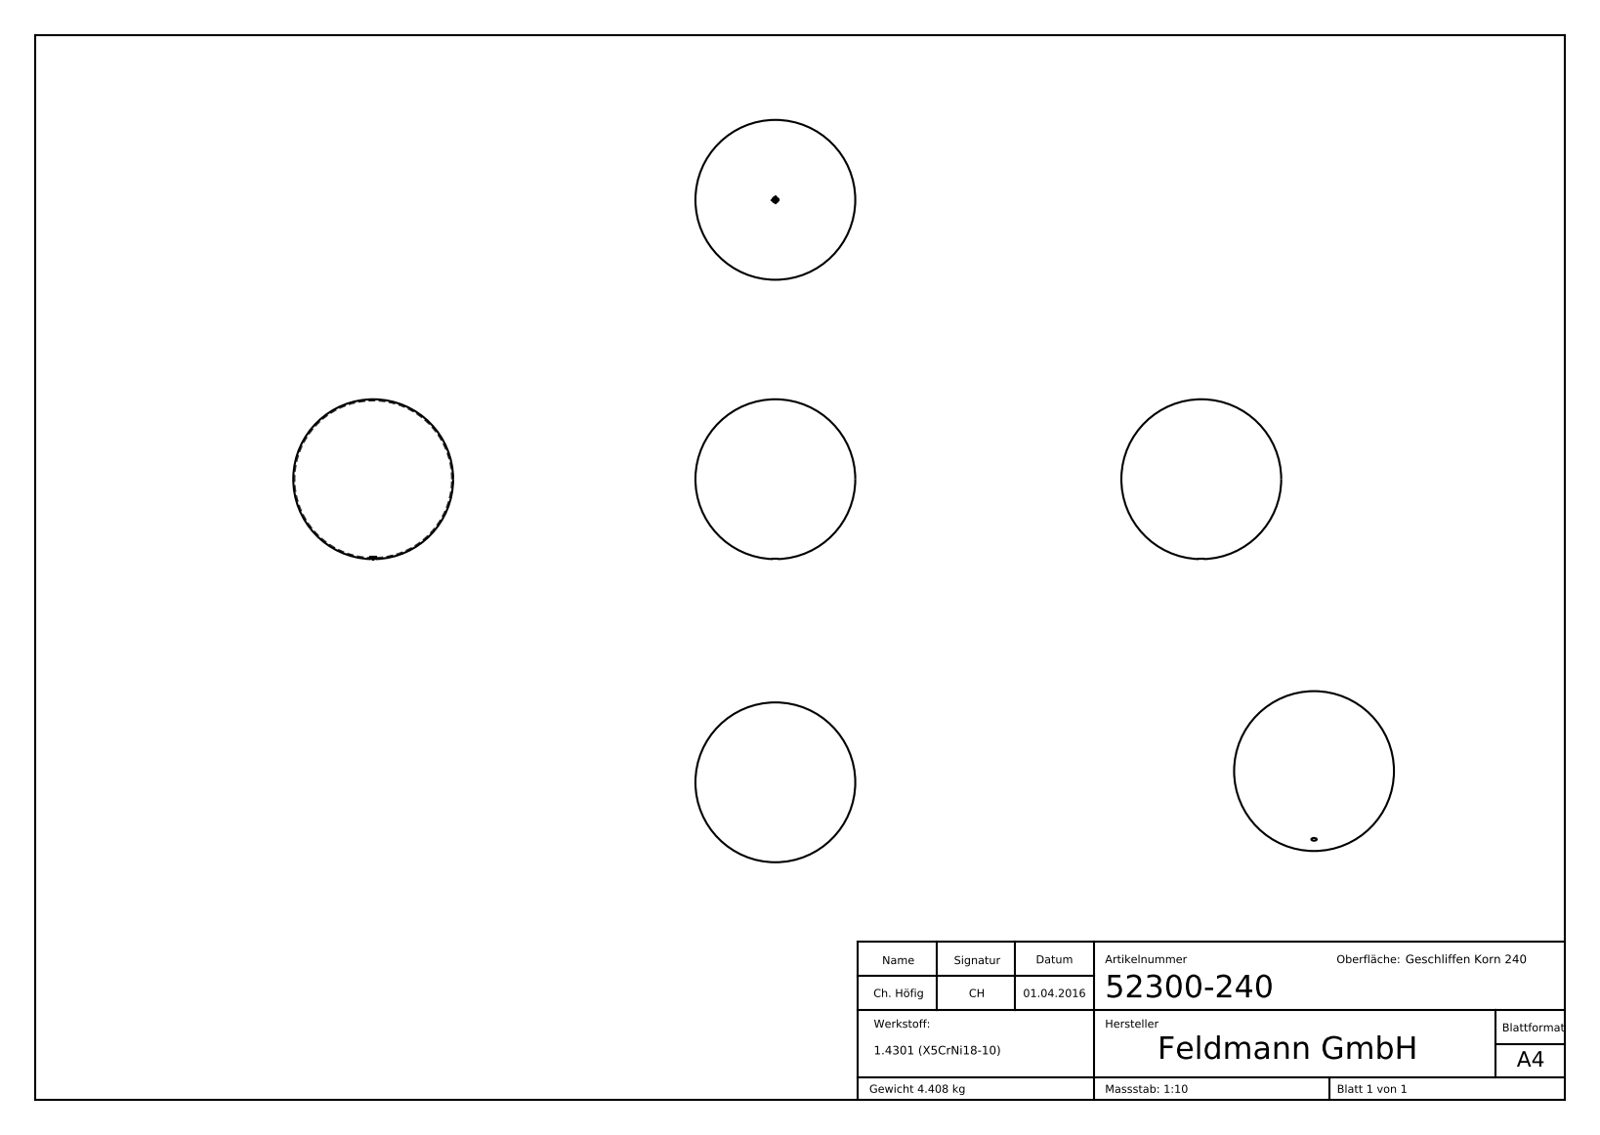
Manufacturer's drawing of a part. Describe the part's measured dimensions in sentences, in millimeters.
The part is named "52300-240". Its 3-D file was written by "SolidWorks 2015 (CONFIG_CONTROL_DESIGN)". It is 1 solid with 236 faces: 93 planar, 4 cylindrical and 139 other. Overall it measures 300 by 300 by 299.93 millimeters. Its volume is 558 032 cubic millimeters and its surface area 558 124 square millimeters. Round holes: 1 of diameter 8.5. Round bosses or shafts: 1 of diameter 12.
